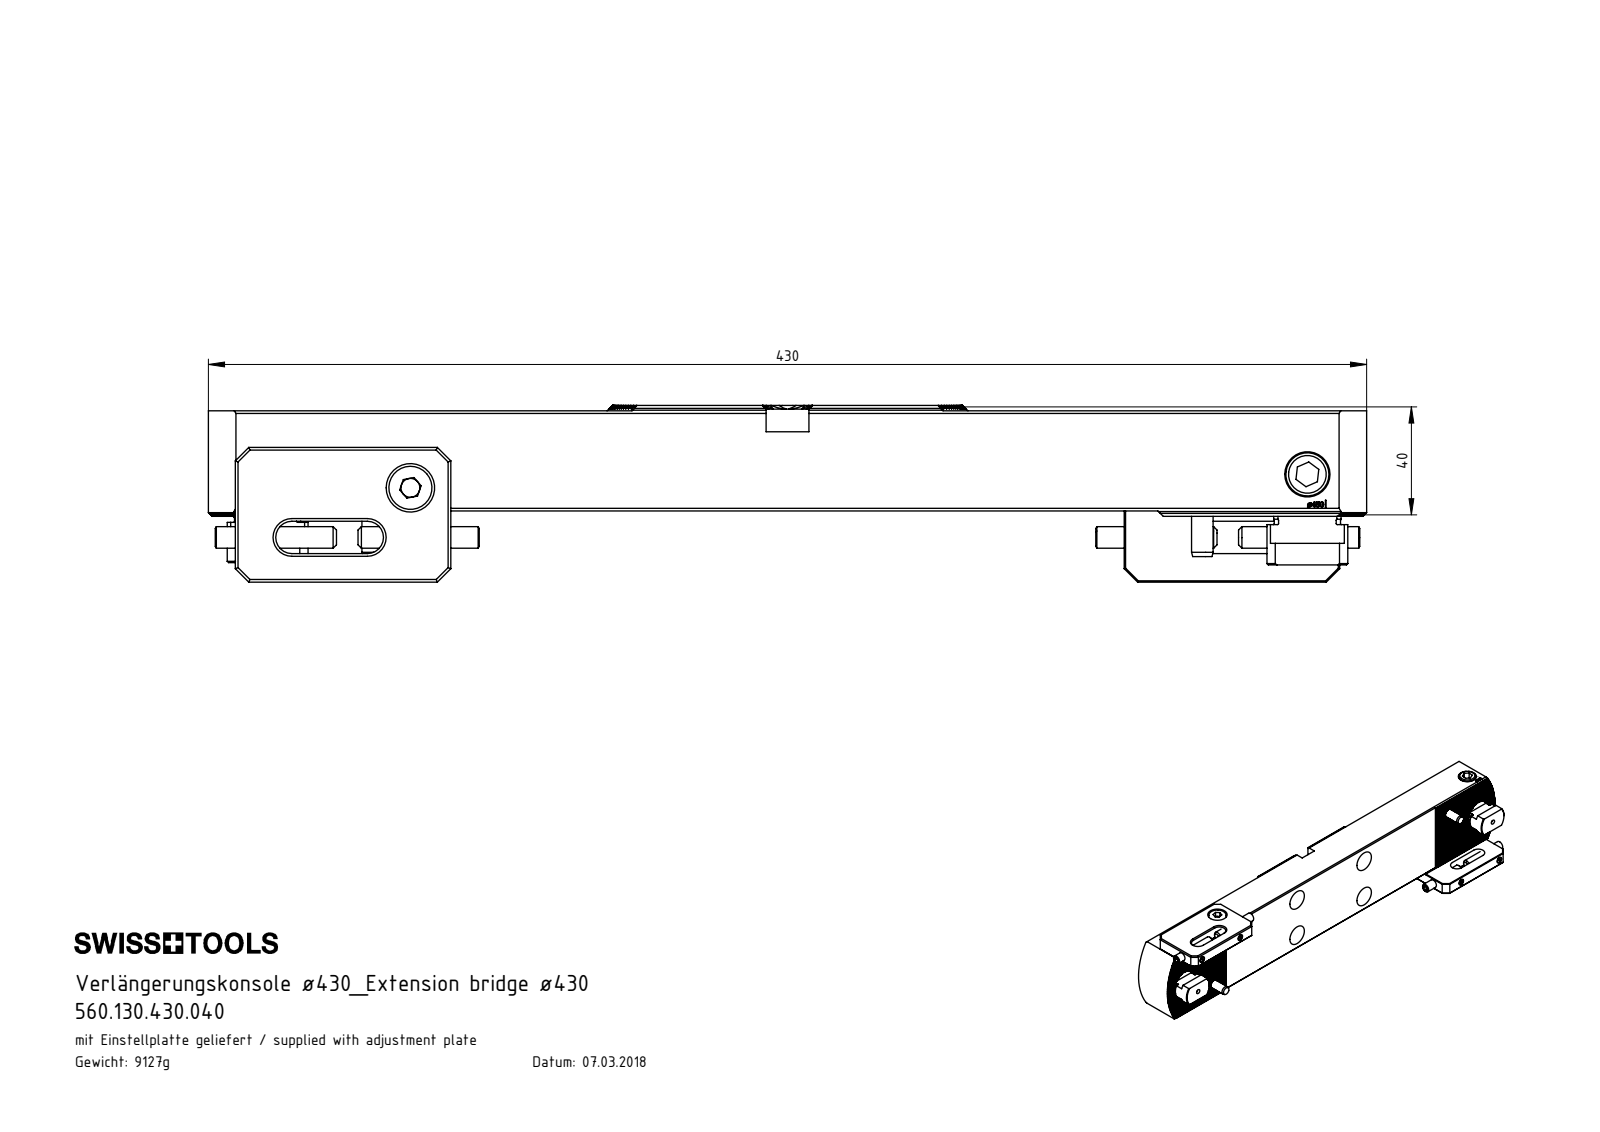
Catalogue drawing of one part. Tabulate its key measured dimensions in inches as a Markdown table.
| quantity | value |
| --- | --- |
| part name | VK1-ER3.001.028_A; VK1-ER7.001.012_mit langer Schraube; ISO 4766 - M6x12_ISO 4766 - M6 x 10; DIN 7984 - M10 x 16 (+8 more) |
| STEP written by | SolidWorks 2017 (CONFIG_CONTROL_DESIGN) |
| units | inches |
| bodies | 27 solids, 1575 faces (890 planar, 402 cylindrical, 283 other) |
| overall size | 16.929 × 3.701 × 2.582 |
| volume | 71.34 in³ |
| surface area | 274.1 in² |
| round holes (diameter × count) | 0.197 × 4, 0.236 × 4, 0.268 × 4, 0.512 × 4, 0.748 × 4, 0.079 × 2, 0.315 × 2, 0.335 × 2, 0.413 × 2, 0.433 × 2, 0.551 × 2, 0.709 × 2 |
| round bosses / shafts (diameter × count) | 0.63 × 4, 0.236 × 4, 0.394 × 2, 0.315 × 2 |
| partial cylindrical surfaces (radius × count) | 0.006 × 66, 0.079 × 8, 0.236 × 4, 0.484 × 2, 0.591 × 2, 2.559 × 2, 0.313 × 1 |
| main face-to-face distances | 1.463, 2.756, 0.472, 3.228, 0.068, 0.341, 0.136, 0.273, 0.02, 0.453 |
| hole center spacings | 5.919, 9.364, 15.197, 0.311, 0.73, 0.772, 1.359, 1.381 |
